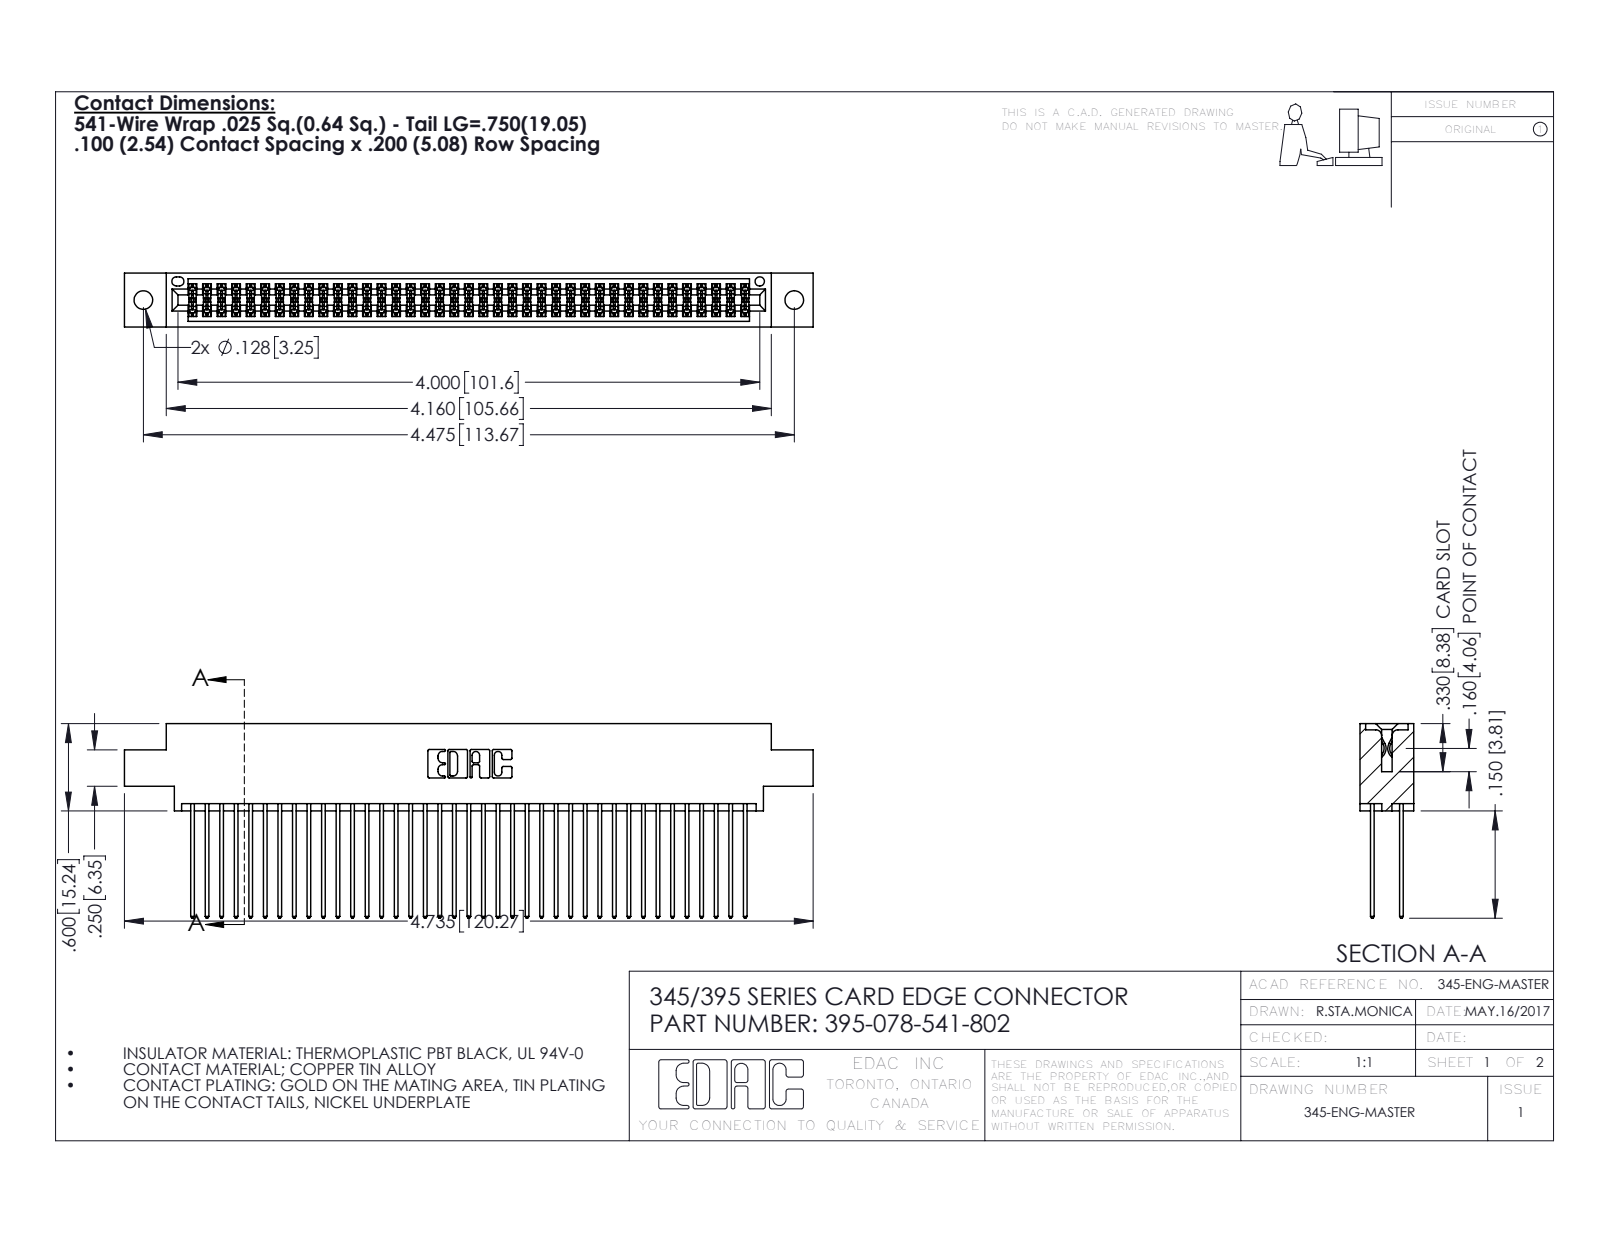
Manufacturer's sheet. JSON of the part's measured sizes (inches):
{"part_name": "345-292-001_345-293-141; 345 Part_0.170 Offset - 0.128 Dia; 395-078-541-802", "step_written_by": "SolidWorks 2016 (CONFIG_CONTROL_DESIGN)", "units": "inches", "bodies": {"solids": 79, "faces": 4030, "planar": 2658, "cylindrical": 1372, "other": 0}, "overall_size": [4.735, 1.337, 0.37], "volume_in3": 0.729, "surface_area_in2": 30.36, "round_holes": [[0.128, 2], [0.064, 1]], "partial_cylinders_radius": [[0.006, 117], [0.01, 78], [0.01, 22], [0.007, 6], [0.031, 6], [0.026, 3], [0.014, 2], [0.019, 2]], "face_to_face_distances": [0.298, 0.072, 0.2, 0.098, 0.272, 0.025, 0.37, 0.225, 0.175, 0.149], "hole_center_spacings": [0.27, 4.239, 4.475]}
